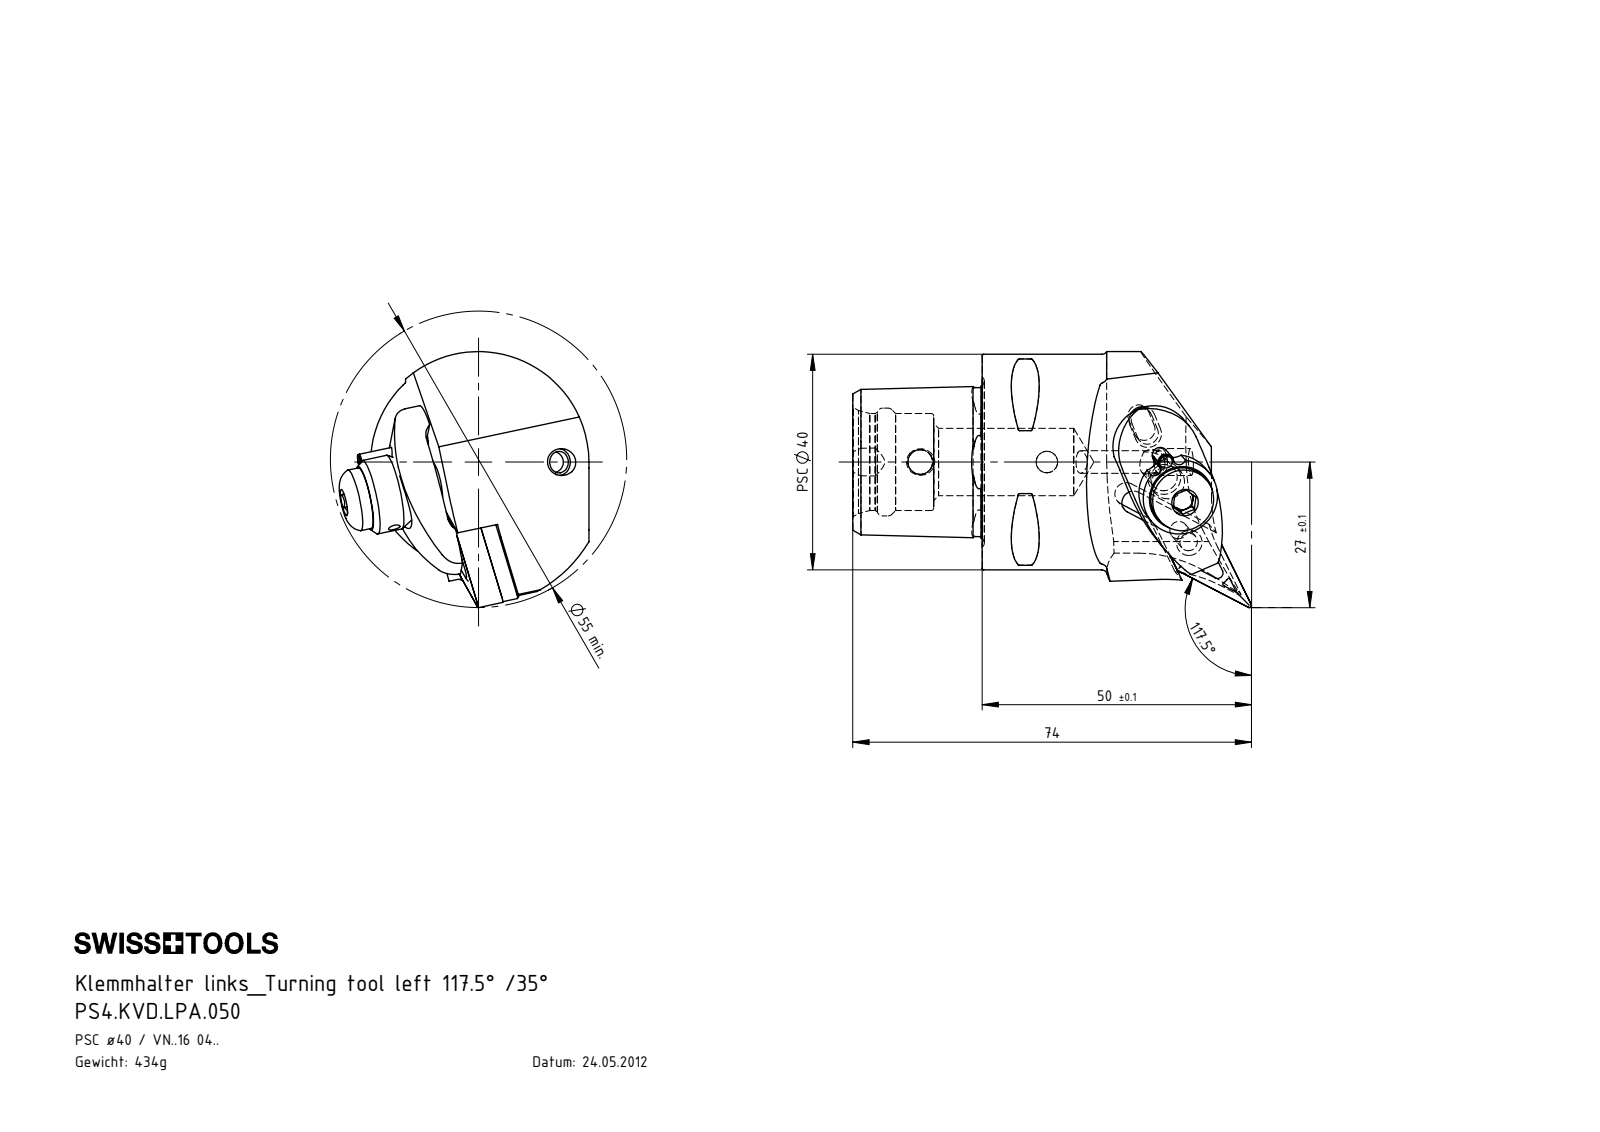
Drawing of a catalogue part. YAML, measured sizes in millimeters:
part_name: "WCC-ER3.102.024_C; PS4.KVD.LPA.050; VNMG160404; WVD-ER2.101.003_A (+7 more)"
step_written_by: "SolidWorks 2017 (AUTOMOTIVE_DESIGN)"
units: millimeters
bodies: {solids: 11, faces: 443, planar: 100, cylindrical: 133, other: 210}
overall_size: [74, 47.5, 46.34]
volume: 54704
surface_area: 17780
round_holes:
  - {diameter: 2, count: 3}
  - {diameter: 4, count: 2}
  - {diameter: 7, count: 2}
  - {diameter: 2.4, count: 1}
  - {diameter: 3, count: 1}
  - {diameter: 3.3, count: 1}
  - {diameter: 3.8, count: 1}
  - {diameter: 4.2, count: 1}
  - {diameter: 4.6, count: 1}
  - {diameter: 4.95, count: 1}
  - {diameter: 5, count: 1}
  - {diameter: 6.2, count: 1}
round_bosses_or_shafts:
  - {diameter: 4, count: 2}
  - {diameter: 3, count: 2}
  - {diameter: 40, count: 1}
  - {diameter: 14, count: 1}
  - {diameter: 11.5, count: 1}
  - {diameter: 6.8, count: 1}
  - {diameter: 6.2, count: 1}
  - {diameter: 6, count: 1}
partial_cylinders:
  - {radius: 0.3, count: 8}
  - {radius: 0.34, count: 6}
  - {radius: 0.59, count: 6}
  - {radius: 0.4, count: 4}
  - {radius: 1.5, count: 3}
  - {radius: 3, count: 3}
  - {radius: 0.5, count: 2}
  - {radius: 2, count: 2}
face_to_face_distances: [4.45, 1.31, 5.76, 24, 8.93, 3.17, 7.62, 15.52, 3.18, 7.63]
hole_center_spacings: [7.22, 0.98, 14.3, 14.31, 21.52, 7.21, 8.19, 8.2]
